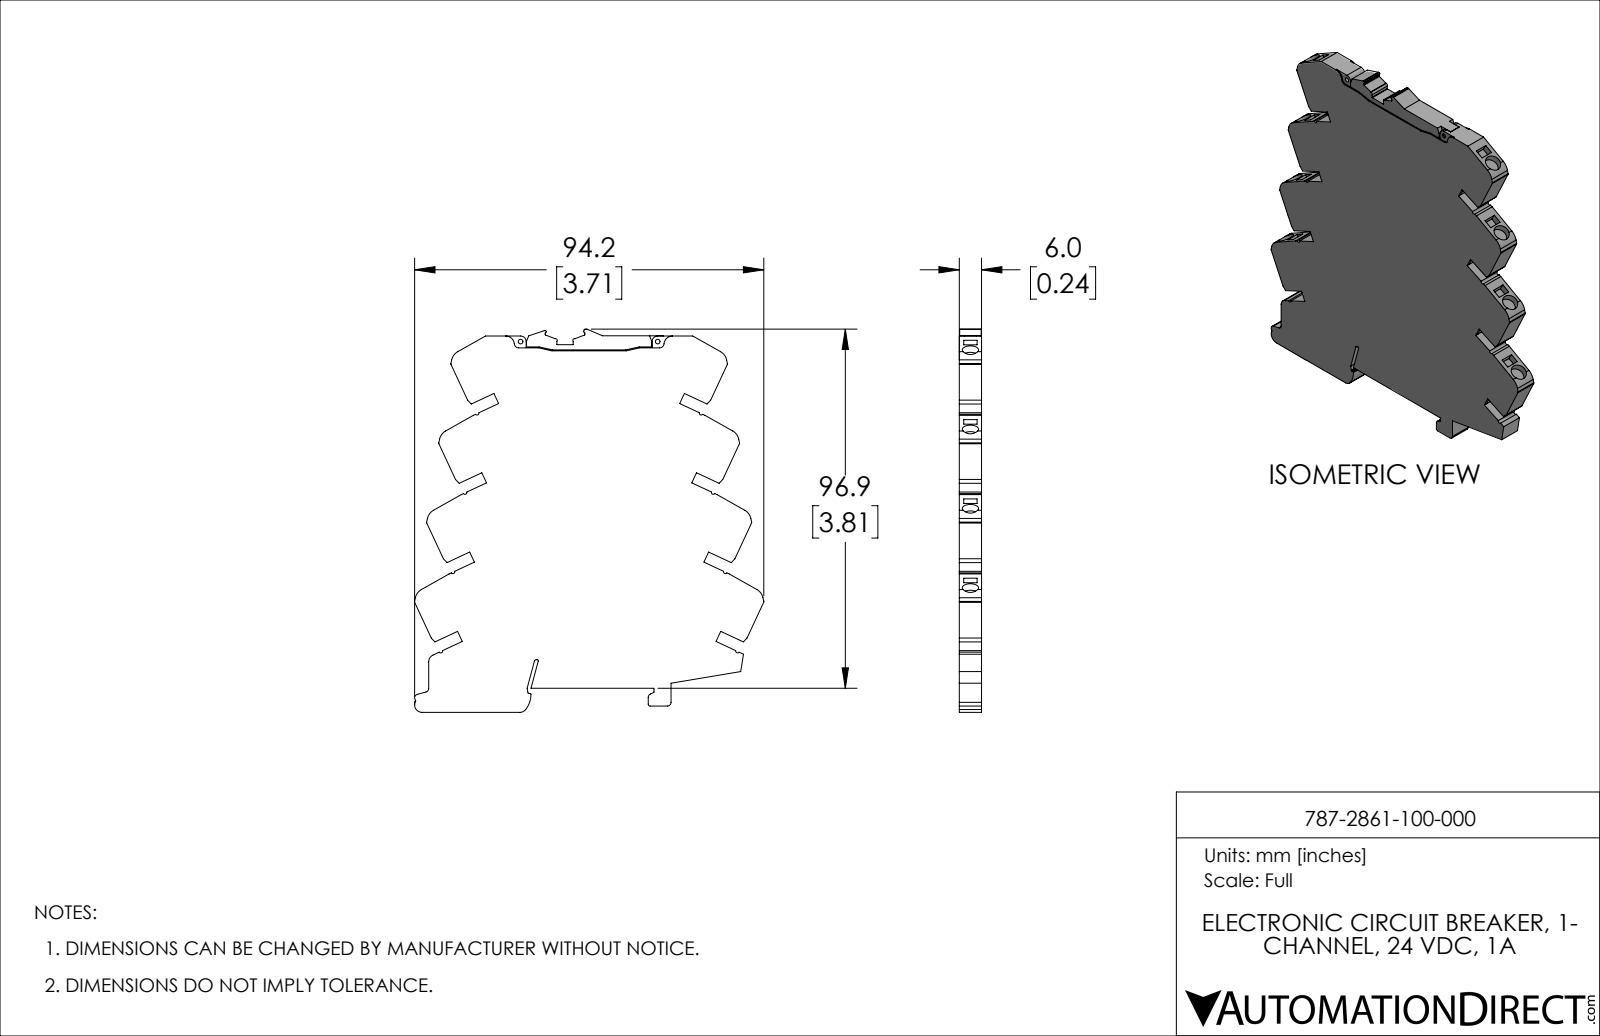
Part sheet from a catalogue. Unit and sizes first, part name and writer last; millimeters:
Units: millimetres
Overall size (bounding box): 103.36 × 94.26 × 6
Round holes (diameter × count): ⌀4.4 ×8, ⌀1.25 ×2
Partial cylindrical surfaces — rounded edges, fillets, slot ends (radius × count): R0.5 ×12, R0.2 ×11, R0.4 ×8, R3.35 ×8, R1 ×4, R0.3 ×3, R2 ×3, R0.45 ×2
Main face-to-face distances: 6, 17.99, 17.02, 12.01, 5.9, 12, 3, 24.01, 35.98, 6.5
Hole centre spacings: 13.35, 13.34, 26.7, 26.69, 26.71, 37, 40.04, 40.05
Volume: 43 932 mm³ · Surface area: 19 262 mm²
Bodies: 1 solid, 294 faces (219 planar, 75 cylindrical, 0 other)
Part name (STEP PRODUCT): 787-2861/100-000
STEP written by: PARTsolutions (CONFIG_CONTROL_DESIGN)
